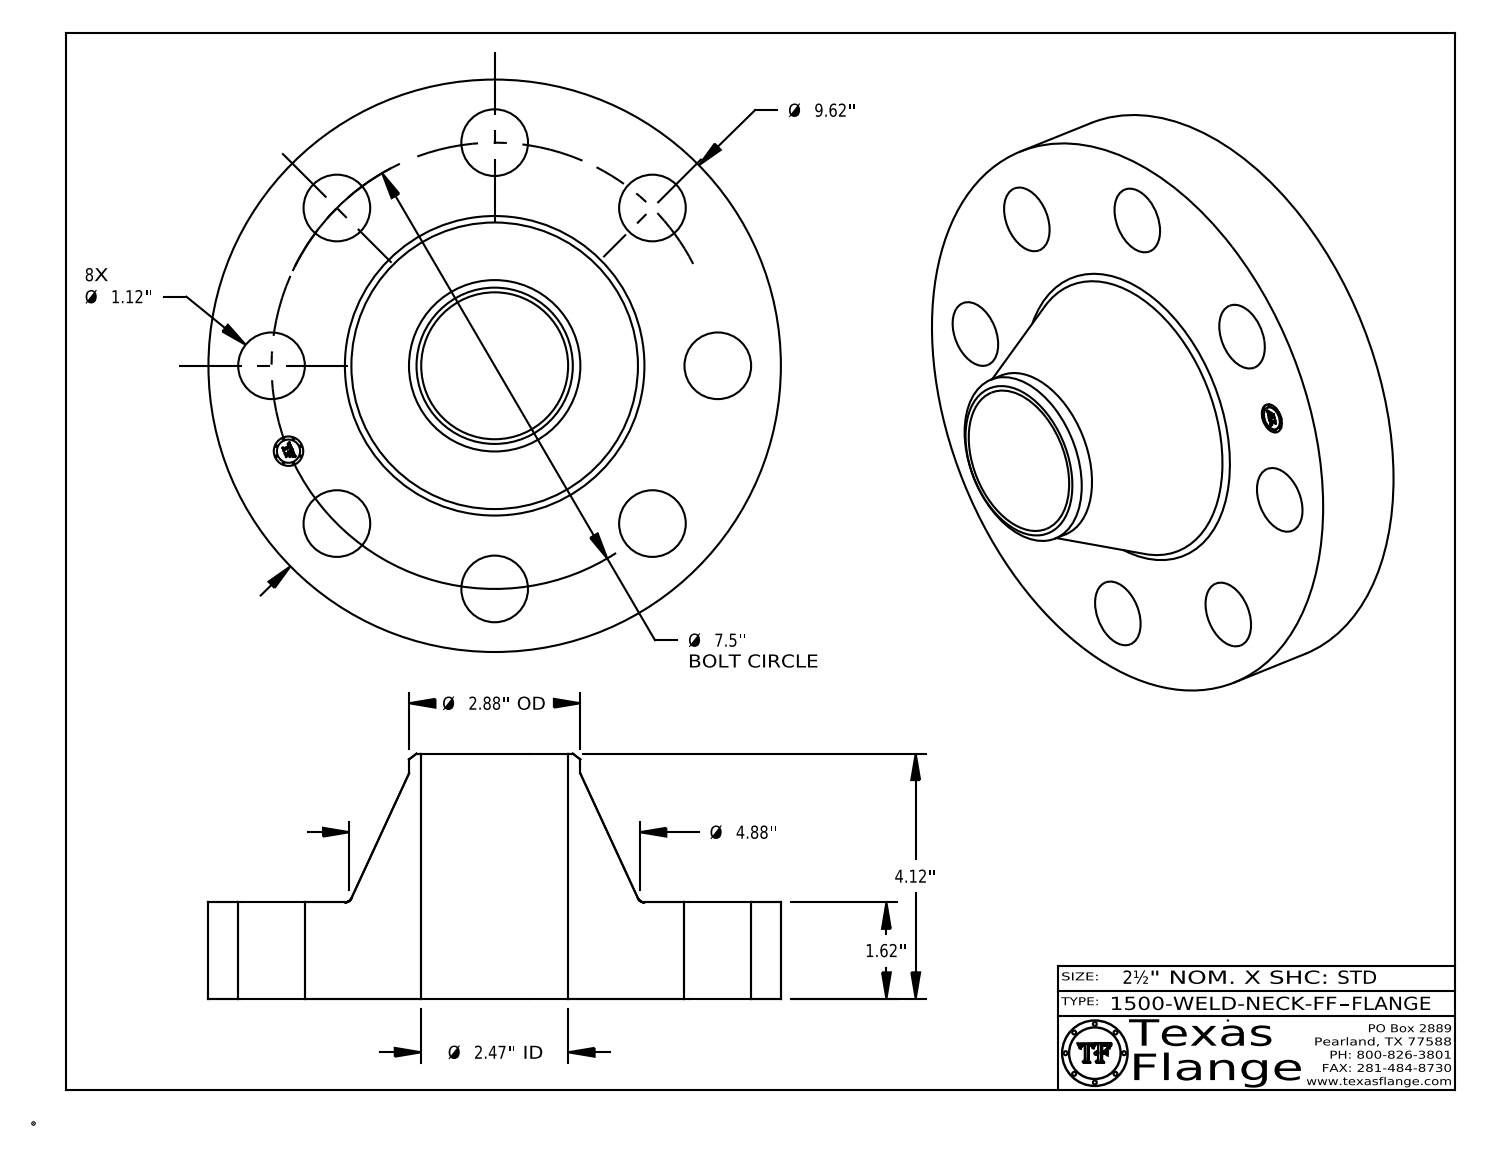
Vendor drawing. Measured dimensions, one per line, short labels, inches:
name: 1500-WELD-NECK-FF
written by: CATIA V5 STEP AP214 (AUTOMOTIVE_DESIGN)
unit: in
bodies: 1 solid, 416 faces (368 planar, 42 cylindrical, 6 other)
size: 9.62 × 9.62 × 4.12
volume: 113.6 in³; area: 265.7 in²
holes: 8× ⌀1.12, 1× ⌀0.495, 1× ⌀2.469
bosses: 8× ⌀0.03, 1× ⌀9.62, 1× ⌀2.88, 1× ⌀0.39
face distances: 1.62, 4.12, 2.5, 0.015, 1.605, 2.515, 0.148, 0.145, 0.027, 0.096
hole spacings: 3.75, 2.87, 5.303, 6.929, 1.463, 6.236, 7.356, 7.5
